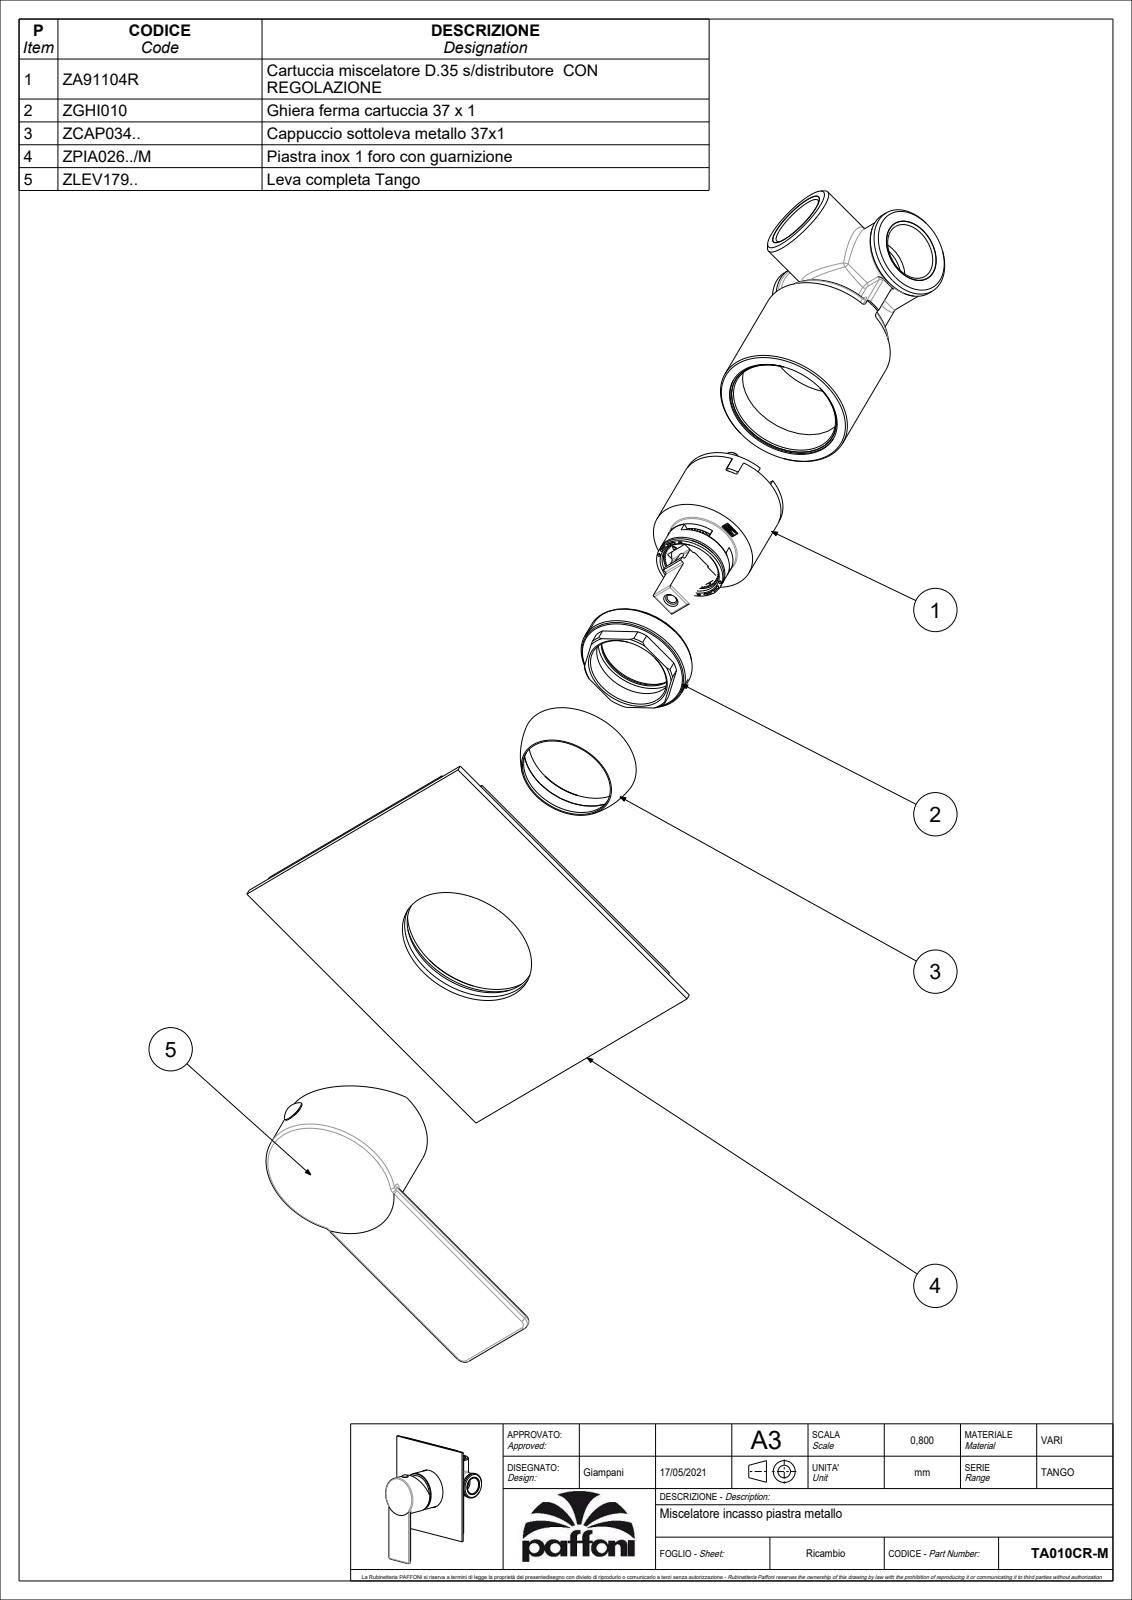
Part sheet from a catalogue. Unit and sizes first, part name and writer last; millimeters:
Units: millimetres
Overall size (bounding box): 135 × 110 × 54.1
Round holes (diameter × count): ⌀3 ×1, ⌀4.2 ×1, ⌀30.6 ×1, ⌀36 ×1, ⌀38 ×1
Round bosses / shafts (diameter × count): ⌀45.5 ×1, ⌀44.8 ×1, ⌀7.6 ×1, ⌀5.5 ×1
Partial cylindrical surfaces — rounded edges, fillets, slot ends (radius × count): R1 ×6, R1.5 ×4, R0.5 ×2, R3 ×2, R3.5 ×1
Main face-to-face distances: 2, 1.96, 48.6, 53.6, 51.6, 3, 50.6, 0.5, 3.5, 50.1
Volume: 54 850 mm³ · Surface area: 51 000 mm²
Bodies: 2 solids, 150 faces (50 planar, 51 cylindrical, 49 other)
Part name (STEP PRODUCT): TA010CR-M
STEP written by: CREO PARAMETRIC BY PTC INC, 2020044 (CONFIG_CONTROL_DESIGN)
